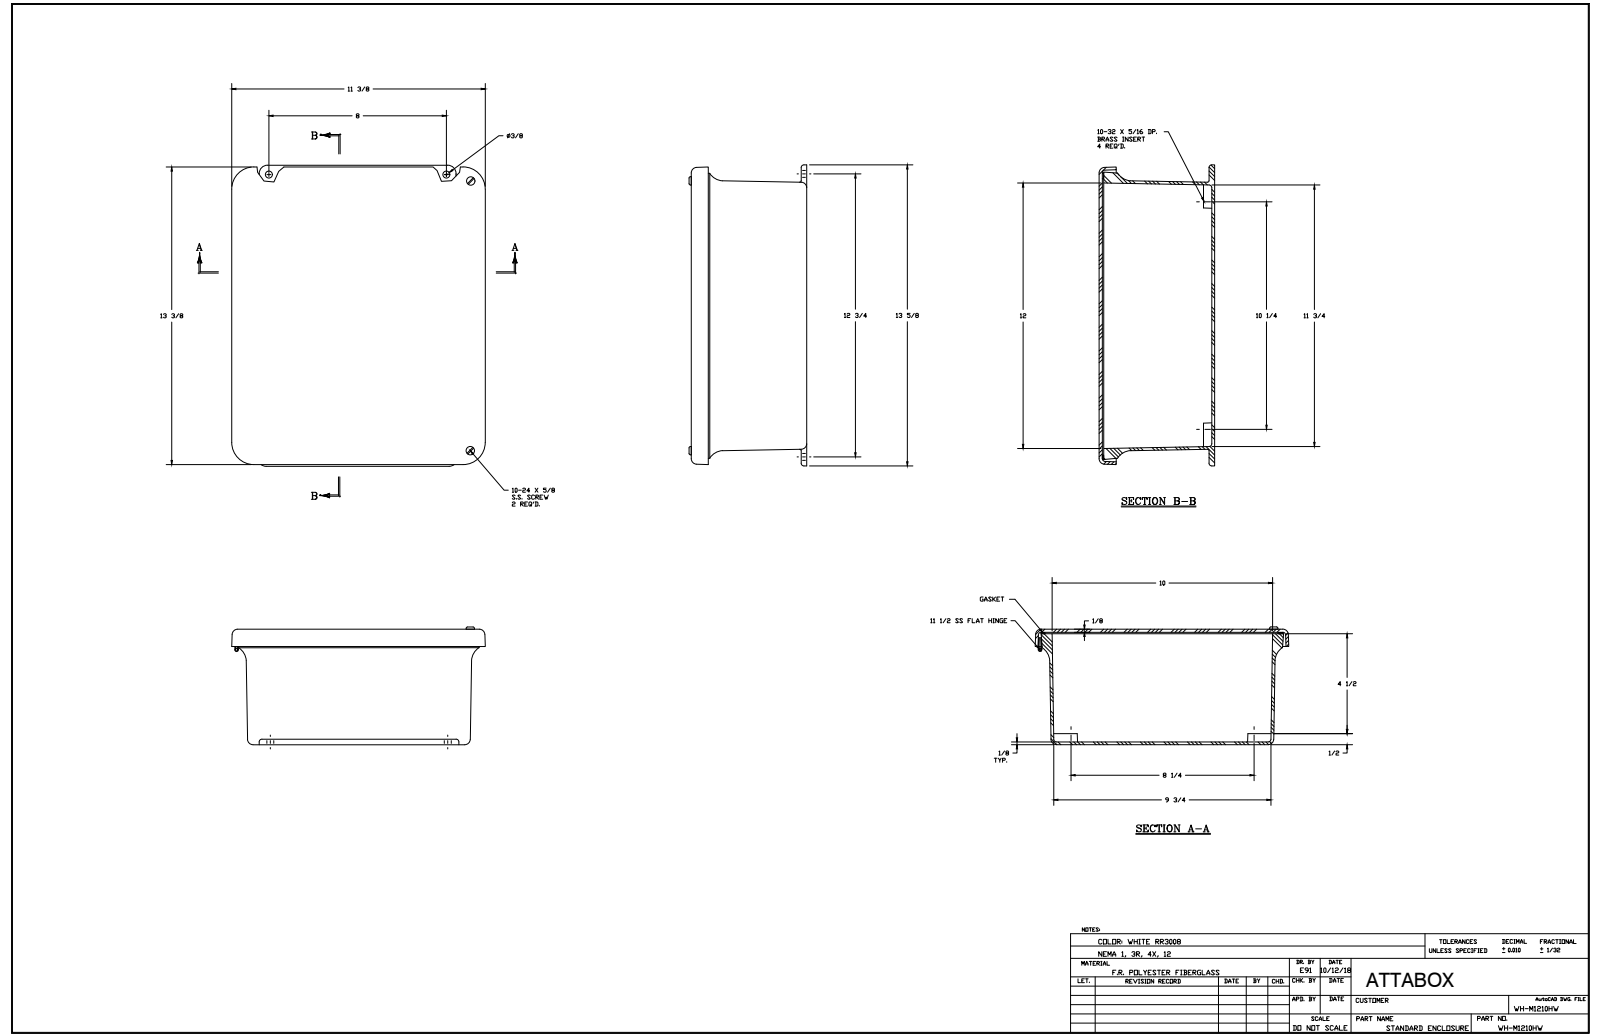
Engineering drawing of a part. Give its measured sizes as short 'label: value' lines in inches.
name: WH-M1210HW
written by: SolidWorks 2018 (AUTOMOTIVE_DESIGN)
unit: in
bodies: 22 solids, 791 faces (283 planar, 303 cylindrical, 205 other)
size: 13.563 × 11.459 × 5.362
volume: 86.62 in³; area: 1 166 in²
holes: 8× ⌀0.131, 8× ⌀0.14, 5× ⌀0.152, 4× ⌀0.156, 4× ⌀0.218, 2× ⌀0.145, 1× ⌀0.085, 1× ⌀0.085
bosses: 8× ⌀0.25, 6× ⌀0.27, 5× ⌀0.125, 3× ⌀0.125, 2× ⌀0.19, 2× ⌀0.156, 1× ⌀0.155
rounds: 20× R0.031, 12× R0.125, 8× R0.25, 4× R0.2, 4× R0.375, 4× R0.75, 2× R0.063
face distances: 0.143, 0.125, 5.088, 5.231, 4.963, 5.106, 5, 0.231, 4.875, 0.088
hole spacings: 3.625, 1.348, 9.252, 11.243, 14.498, 0.25, 3.625, 6.875
